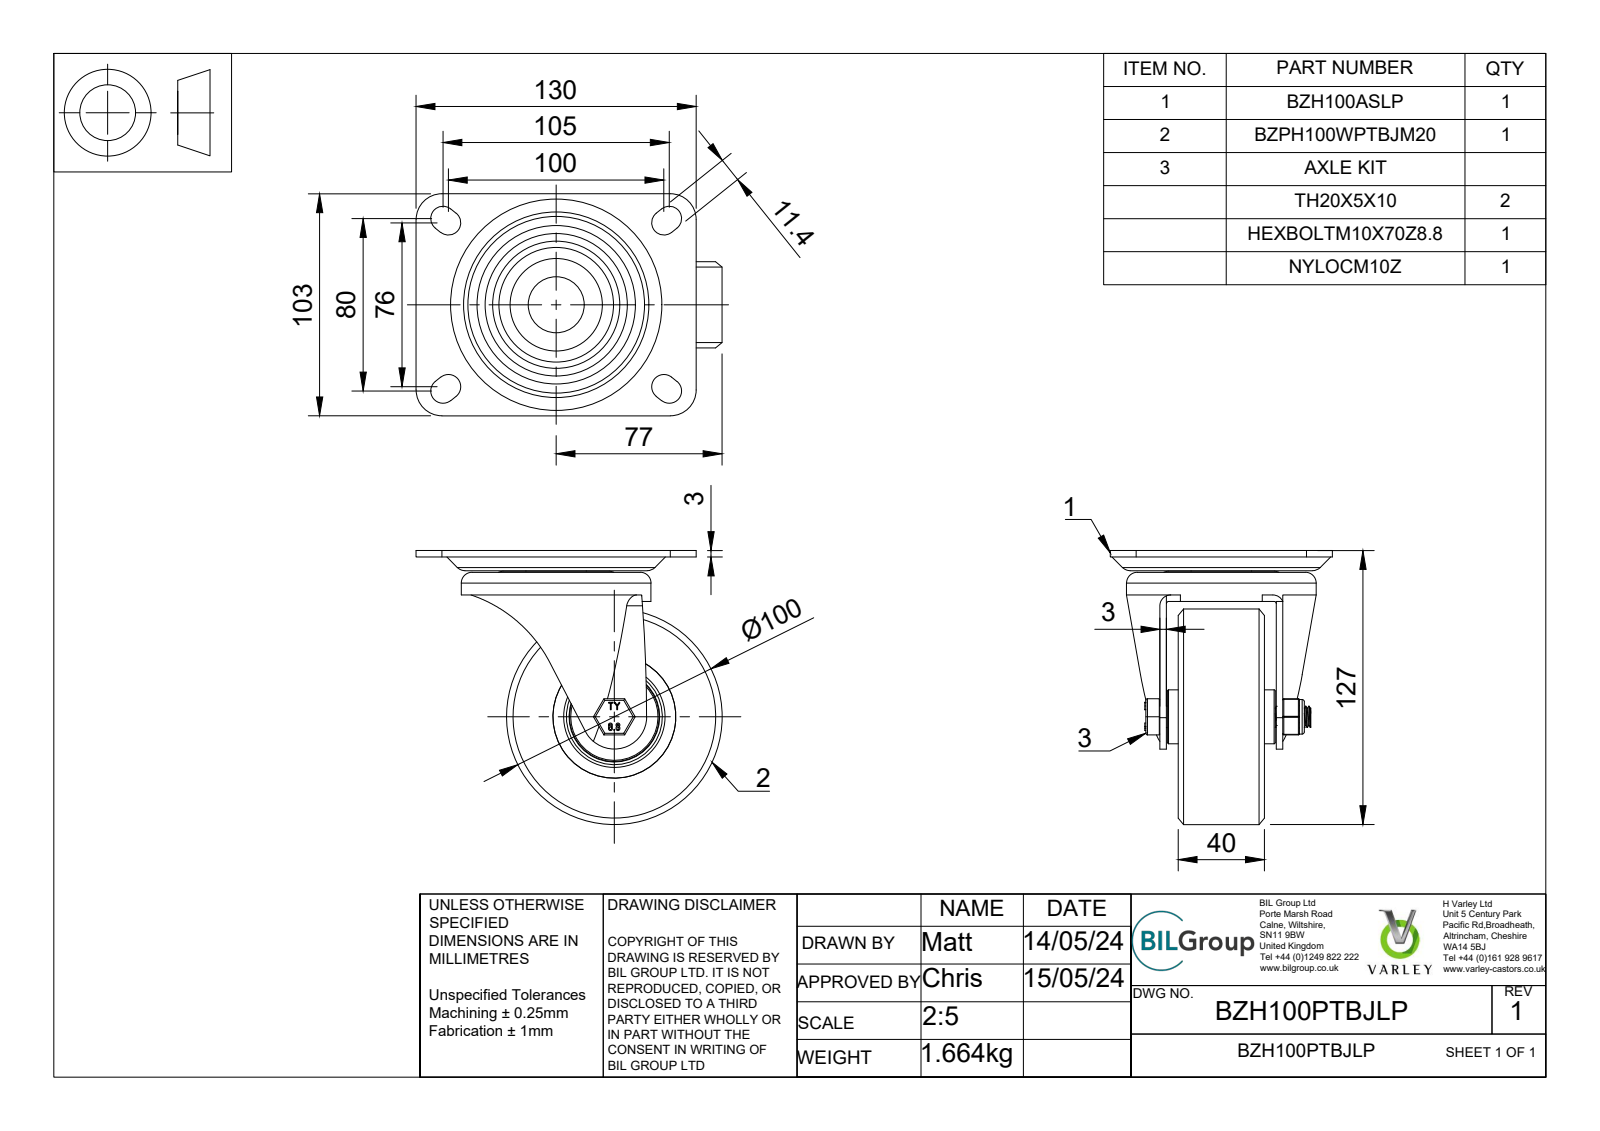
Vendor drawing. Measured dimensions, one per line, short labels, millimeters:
name: BZH100PTBJLP v3; BZPH100WPTBJM20 v1; POLYURETHANE TYRE; CAST IRON RIM (+7 more)
written by: Autodesk Translation Framework v13.14.0.145 (AUTOMOTIVE_DESIGN)
unit: mm
bodies: 36 solids, 1270 faces (575 planar, 260 cylindrical, 435 other)
size: 142 × 127.13 × 103
volume: 397 732 mm³; area: 153 282 mm²
holes: 1× ⌀10, 1× ⌀10.5, 1× ⌀12, 1× ⌀20, 1× ⌀28.5, 1× ⌀30, 1× ⌀41.5, 1× ⌀42, 1× ⌀44, 1× ⌀47, 1× ⌀57, 1× ⌀82
bosses: 1× ⌀100, 1× ⌀88, 1× ⌀40.5, 1× ⌀40, 1× ⌀36, 1× ⌀30, 1× ⌀29, 1× ⌀28
rounds: 18× R0.5, 8× R4, 8× R5.7, 8× R6, 6× R0.75, 4× R12, 2× R1, 2× R5
face distances: 3, 26, 40, 0.5, 13.5, 31.5, 14, 19.5, 5.5, 13.75
